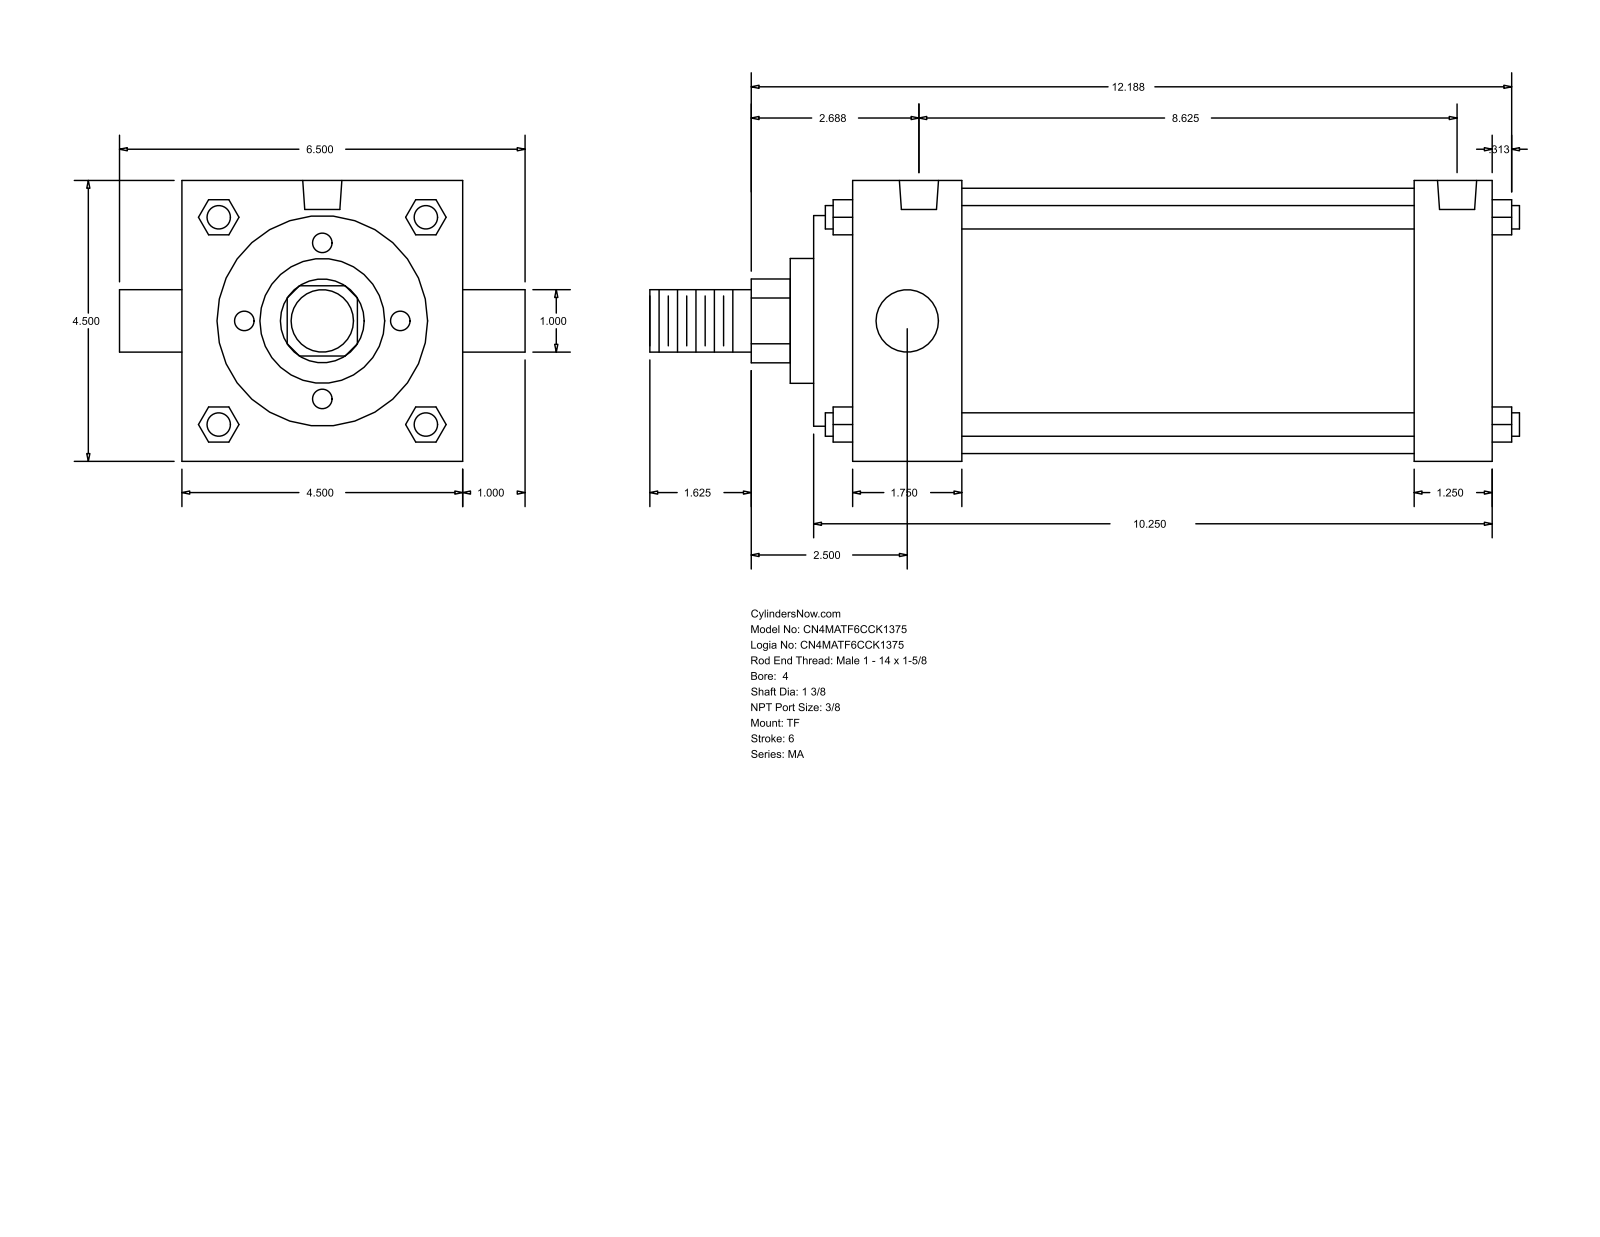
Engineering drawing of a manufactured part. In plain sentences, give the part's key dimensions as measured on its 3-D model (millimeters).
The part is named "MA_TF__0400_1.375". Its 3-D file was written by "GSSL Pune (CONFIG_CONTROL_DESIGN)". It is 0 solids with 122 faces: 93 planar, 29 cylindrical and 0 other. Overall it measures 354.01 by 165.1 by 114.3 millimeters. Round holes: 3 of diameter 11.11, 2 of diameter 15.93. Round bosses or shafts: 4 of diameter 9.53, 2 of diameter 25.4, 1 of diameter 107.95, 1 of diameter 85.72, 1 of diameter 50.8, 1 of diameter 34.92. Partial cylindrical surfaces (rounded edges, fillets, slot ends): 1 of radius 17.06. The main face-to-face distances are 114.3, 260.35, 276.22, 15.87, 244.48, 228.61, 31.74, 60.32, 44.45, 184.16. The hole center spacings are 4.77, 214.31, 209.54, 219.08.
